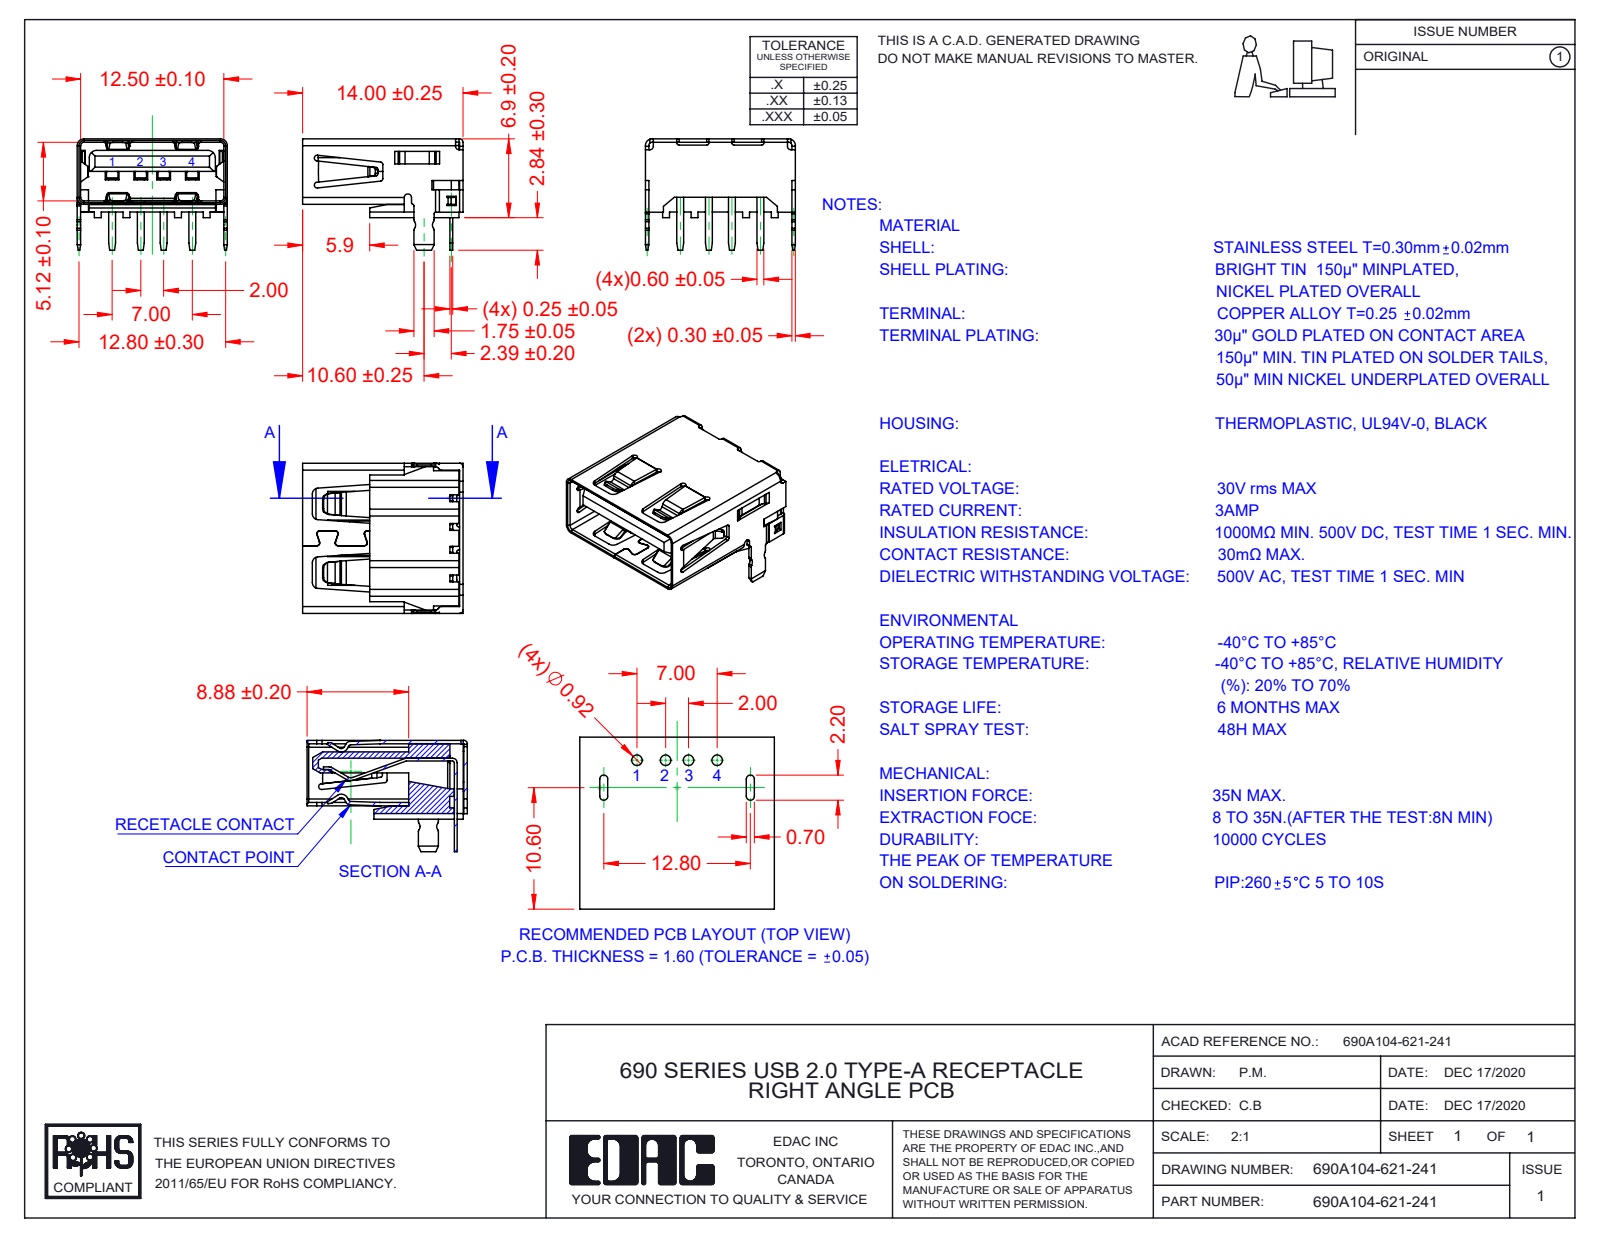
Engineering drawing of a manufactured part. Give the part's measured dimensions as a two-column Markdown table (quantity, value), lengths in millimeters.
| quantity | value |
| --- | --- |
| part name | Insulator 690A104-621-241; Contact 690A104-621-241; 690A104-621-241; Shell 690A104-621-241 |
| STEP written by | SolidWorks 2020 (AUTOMOTIVE_DESIGN) |
| units | millimeters |
| bodies | 6 solids, 929 faces (632 planar, 201 cylindrical, 96 other) |
| overall size | 14 × 13.1 × 9.73 |
| volume | 566 mm³ |
| surface area | 2 083 mm² |
| partial cylindrical surfaces (radius × count) | 0.3 × 24, 0.5 × 24, 0.2 × 22, 0.25 × 13, 0.6 × 10, 0.1 × 9, 0.8 × 7, 0.15 × 4 |
| main face-to-face distances | 5.42, 5.12, 12.8, 1.01, 1.26, 0.55, 1.56, 0.71, 4.16, 4.71 |
